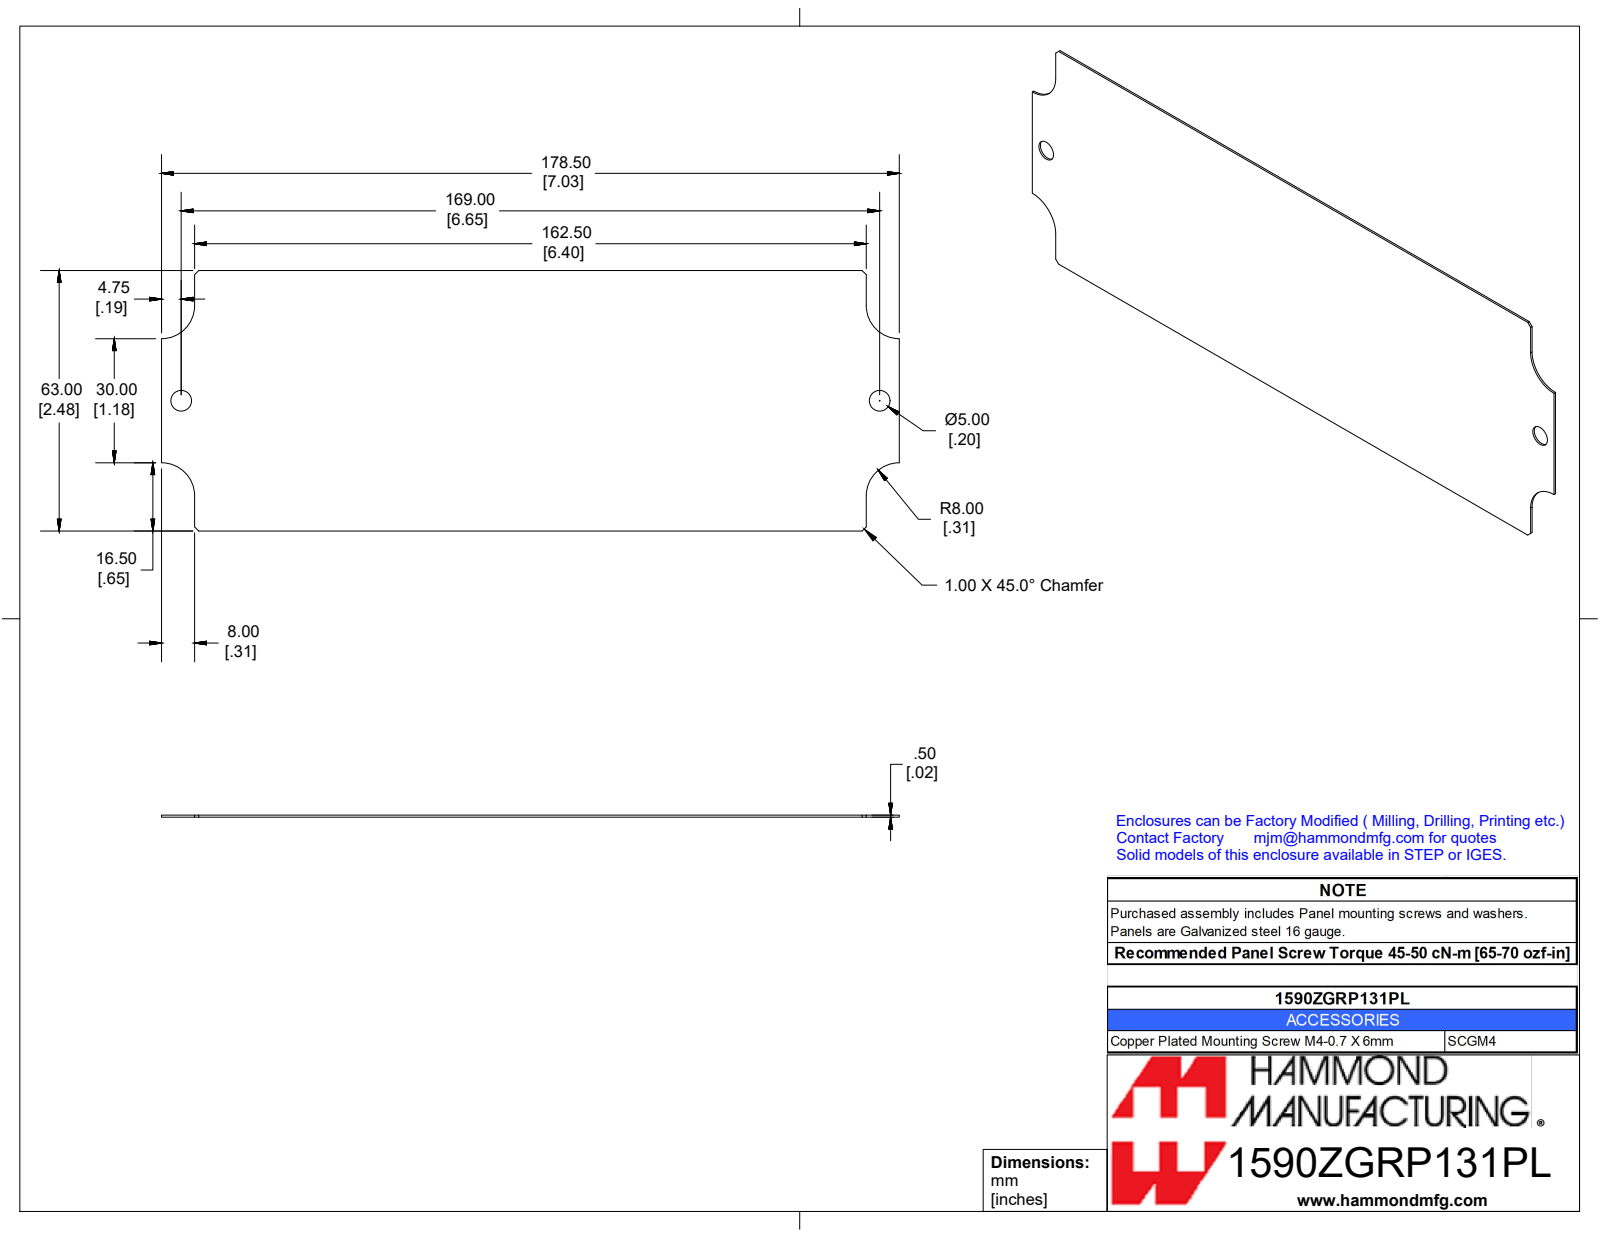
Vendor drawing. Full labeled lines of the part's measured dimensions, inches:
Part name (STEP PRODUCT): 1590ZGRP131PL
STEP written by: SolidWorks 2019 (CONFIG_CONTROL_DESIGN)
Units: inches
Bodies: 1 solid, 20 faces (14 planar, 6 cylindrical, 0 other)
Overall size (bounding box): 7.028 × 2.48 × 0.02
Volume: 0.327 in³ · Surface area: 33.65 in²
Round holes (diameter × count): ⌀0.197 ×2
Partial cylindrical surfaces — rounded edges, fillets, slot ends (radius × count): R0.315 ×4
Main face-to-face distances: 0.02, 2.48, 7.028, 0.315, 6.713, 6.398, 6.221
Hole centre spacings: 6.654
